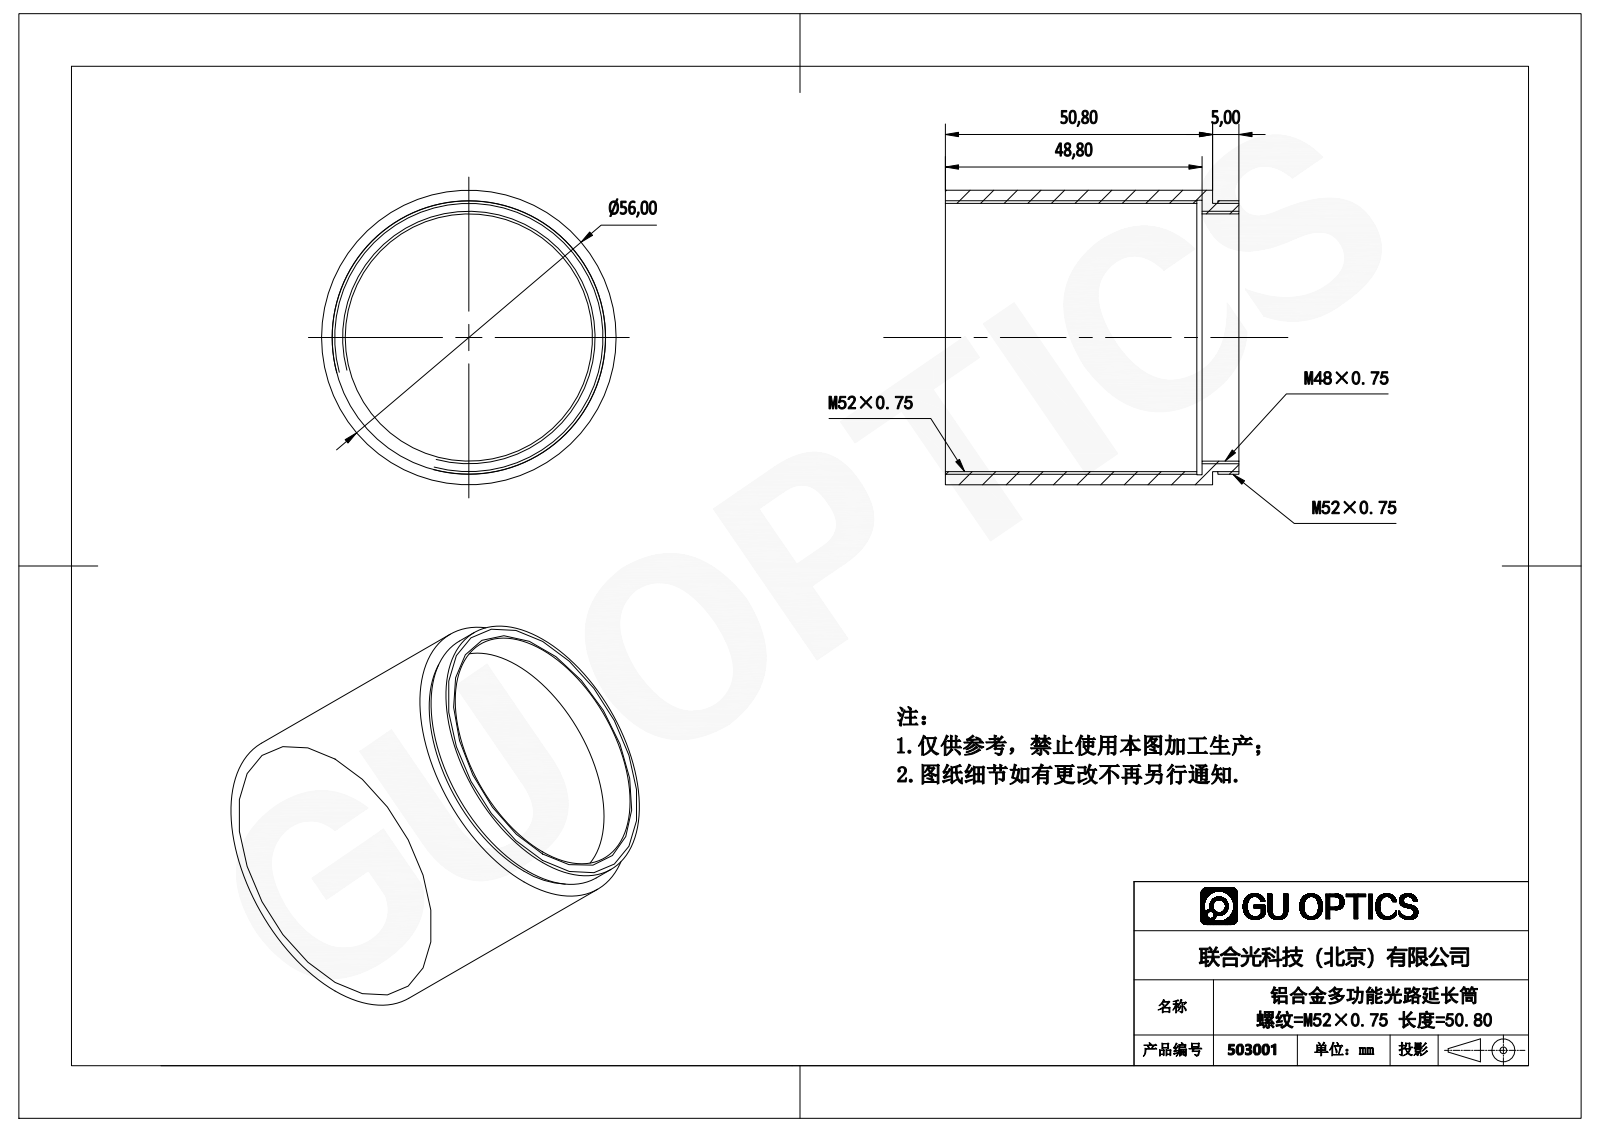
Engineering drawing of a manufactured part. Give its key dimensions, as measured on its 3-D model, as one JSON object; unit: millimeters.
{"part_name": "503001", "step_written_by": "SolidWorks 2016 (AUTOMOTIVE_DESIGN)", "units": "millimeters", "bodies": {"solids": 1, "faces": 18, "planar": 6, "cylindrical": 12, "other": 0}, "overall_size": [56, 56, 55.8], "volume_mm3": 23727, "surface_area_mm2": 20419, "round_holes": [[47, 1], [51, 1], [52.2, 1]], "round_bosses_or_shafts": [[56, 1], [52, 1]], "face_to_face_distances": [50.8, 48.8, 2, 55.8, 7, 5, 1, 3, 4, 47.8]}
